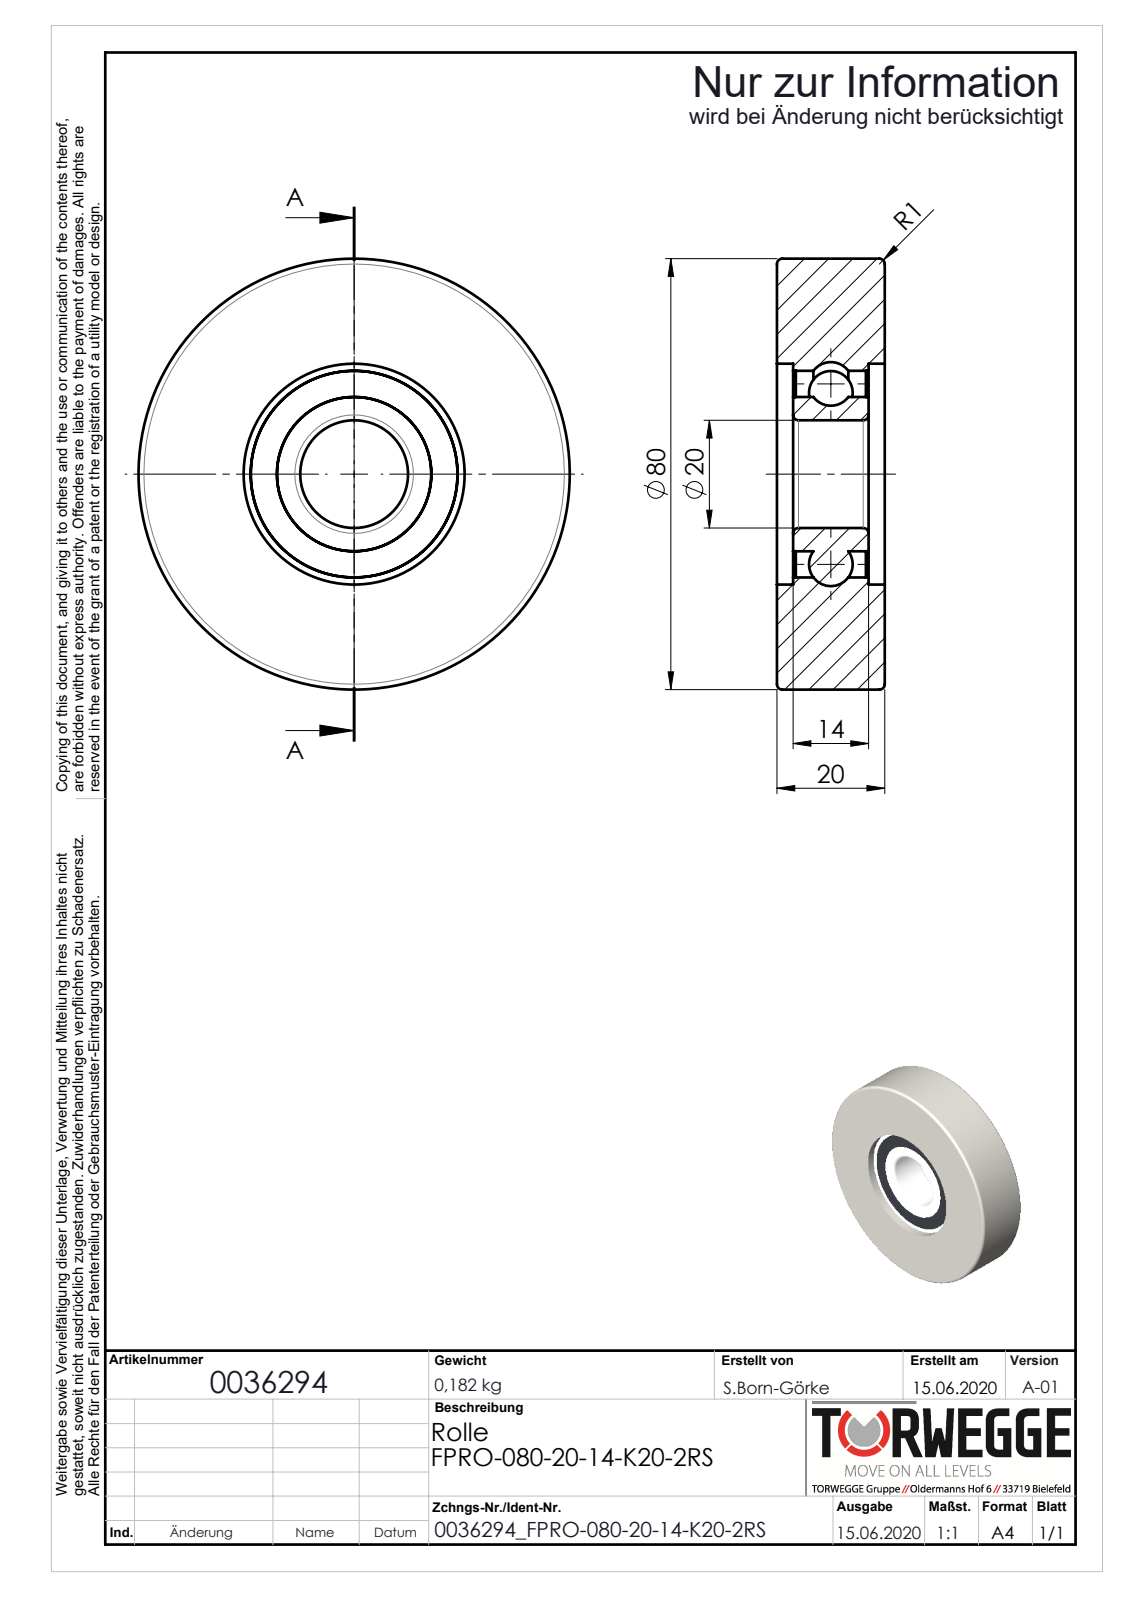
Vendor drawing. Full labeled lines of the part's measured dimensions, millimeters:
Part name (STEP PRODUCT): 0036294
STEP written by: SolidWorks 2018 (AUTOMOTIVE_DESIGN)
Units: millimetres
Bodies: 3 solids, 80 faces (10 planar, 24 cylindrical, 46 other)
Overall size (bounding box): 80 × 80 × 20
Volume: 81 837 mm³ · Surface area: 21 668 mm²
Round holes (diameter × count): ⌀20 ×1, ⌀28.64 ×1, ⌀38.36 ×1, ⌀41 ×1
Round bosses / shafts (diameter × count): ⌀80 ×1
Main face-to-face distances: 20, 3, 17, 3.5, 16.5, 0.5, 13.5, 14, 13
